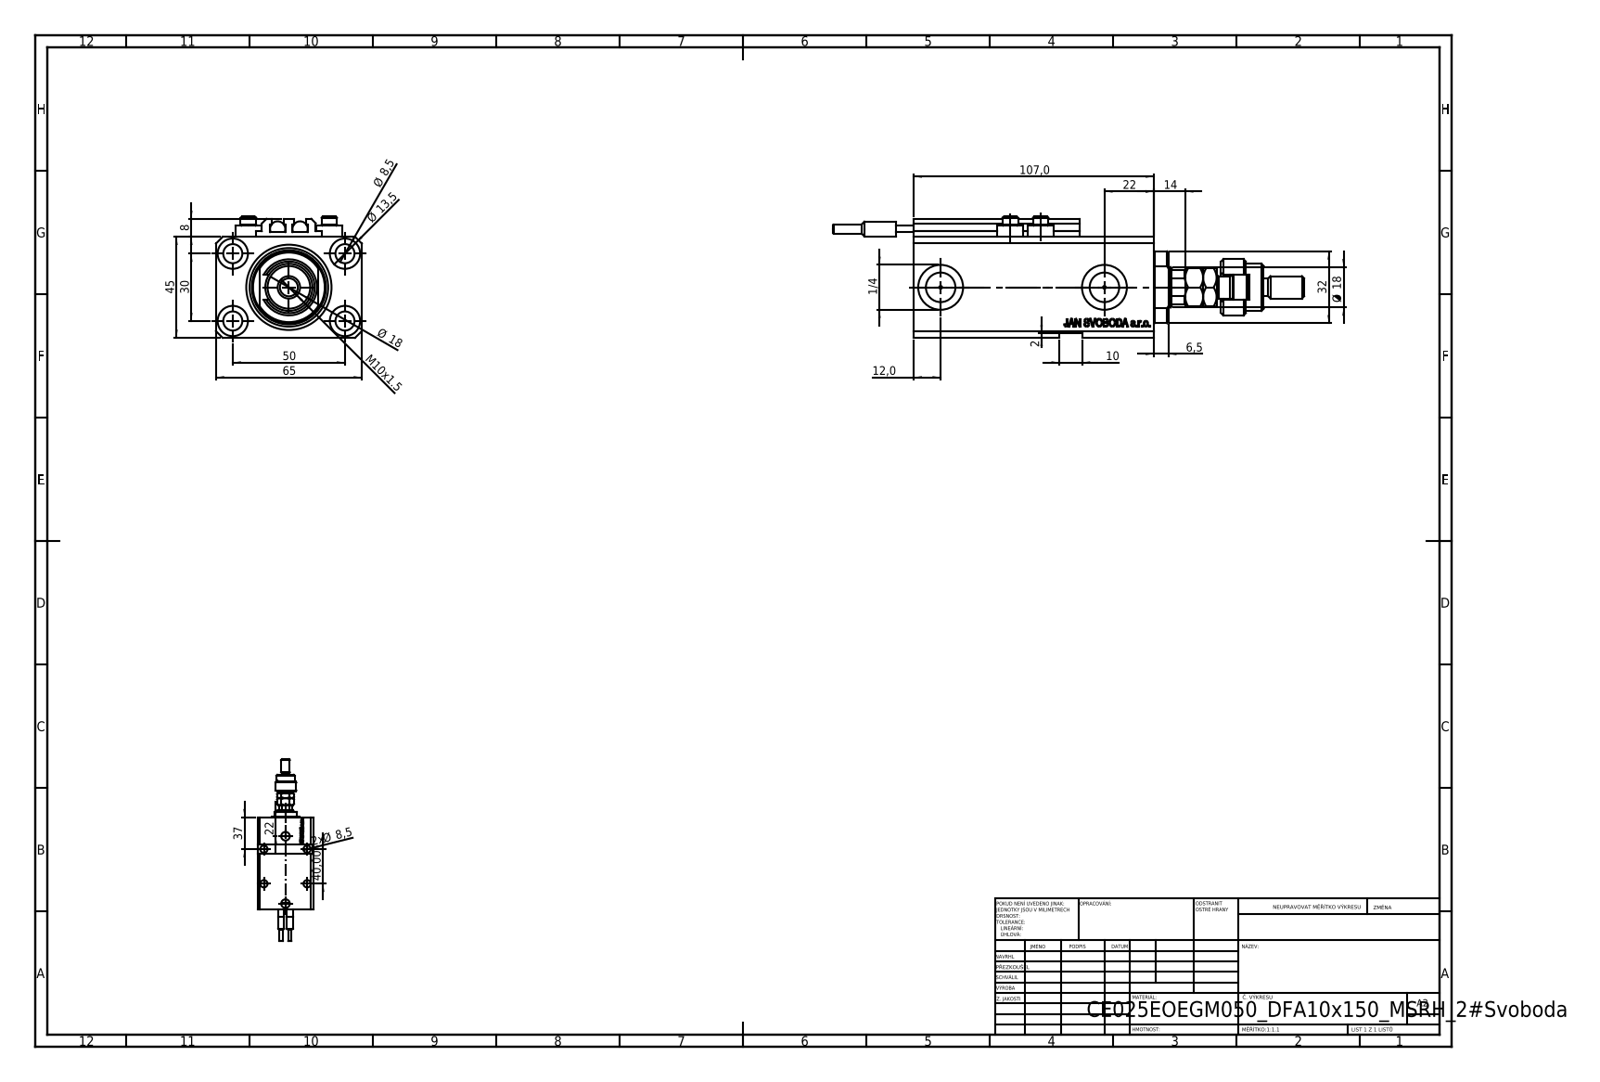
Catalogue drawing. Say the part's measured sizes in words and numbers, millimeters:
The part is named "MFA; V250CE_C_VCP; SWITCH_V250CE; FEMALE_PART_FOR_DFA (+3 more)". Its 3-D file was written by "SolidWorks 2019 (CONFIG_CONTROL_DESIGN)". It is 12 solids with 1224 faces: 571 planar, 171 cylindrical and 482 other. Overall it measures 210 by 65 by 54 millimeters. Its volume is 288 767 cubic millimeters and its surface area 85 071 square millimeters. Round holes: 9 of diameter 8.5, 4 of diameter 1.25, 4 of diameter 4, 4 of diameter 13.5, 2 of diameter 10, 2 of diameter 13.16, 2 of diameter 20, 1 of diameter 18, 1 of diameter 38. Round bosses or shafts: 4 of diameter 11.6, 4 of diameter 7, 2 of diameter 6.8, 2 of diameter 6.5, 2 of diameter 4, 1 of diameter 25, 1 of diameter 21, 1 of diameter 16. Partial cylindrical surfaces (rounded edges, fillets, slot ends): 10 of radius 0.2, 1 of radius 5.5, 1 of radius 8.5, 1 of radius 8.75, 1 of radius 16. The main face-to-face distances are 45, 65, 14, 2, 47, 3, 93, 107, 5, 10. The hole center spacings are 29.15, 50, 13.6, 14.76, 15.12, 27.51, 27.89, 30.
